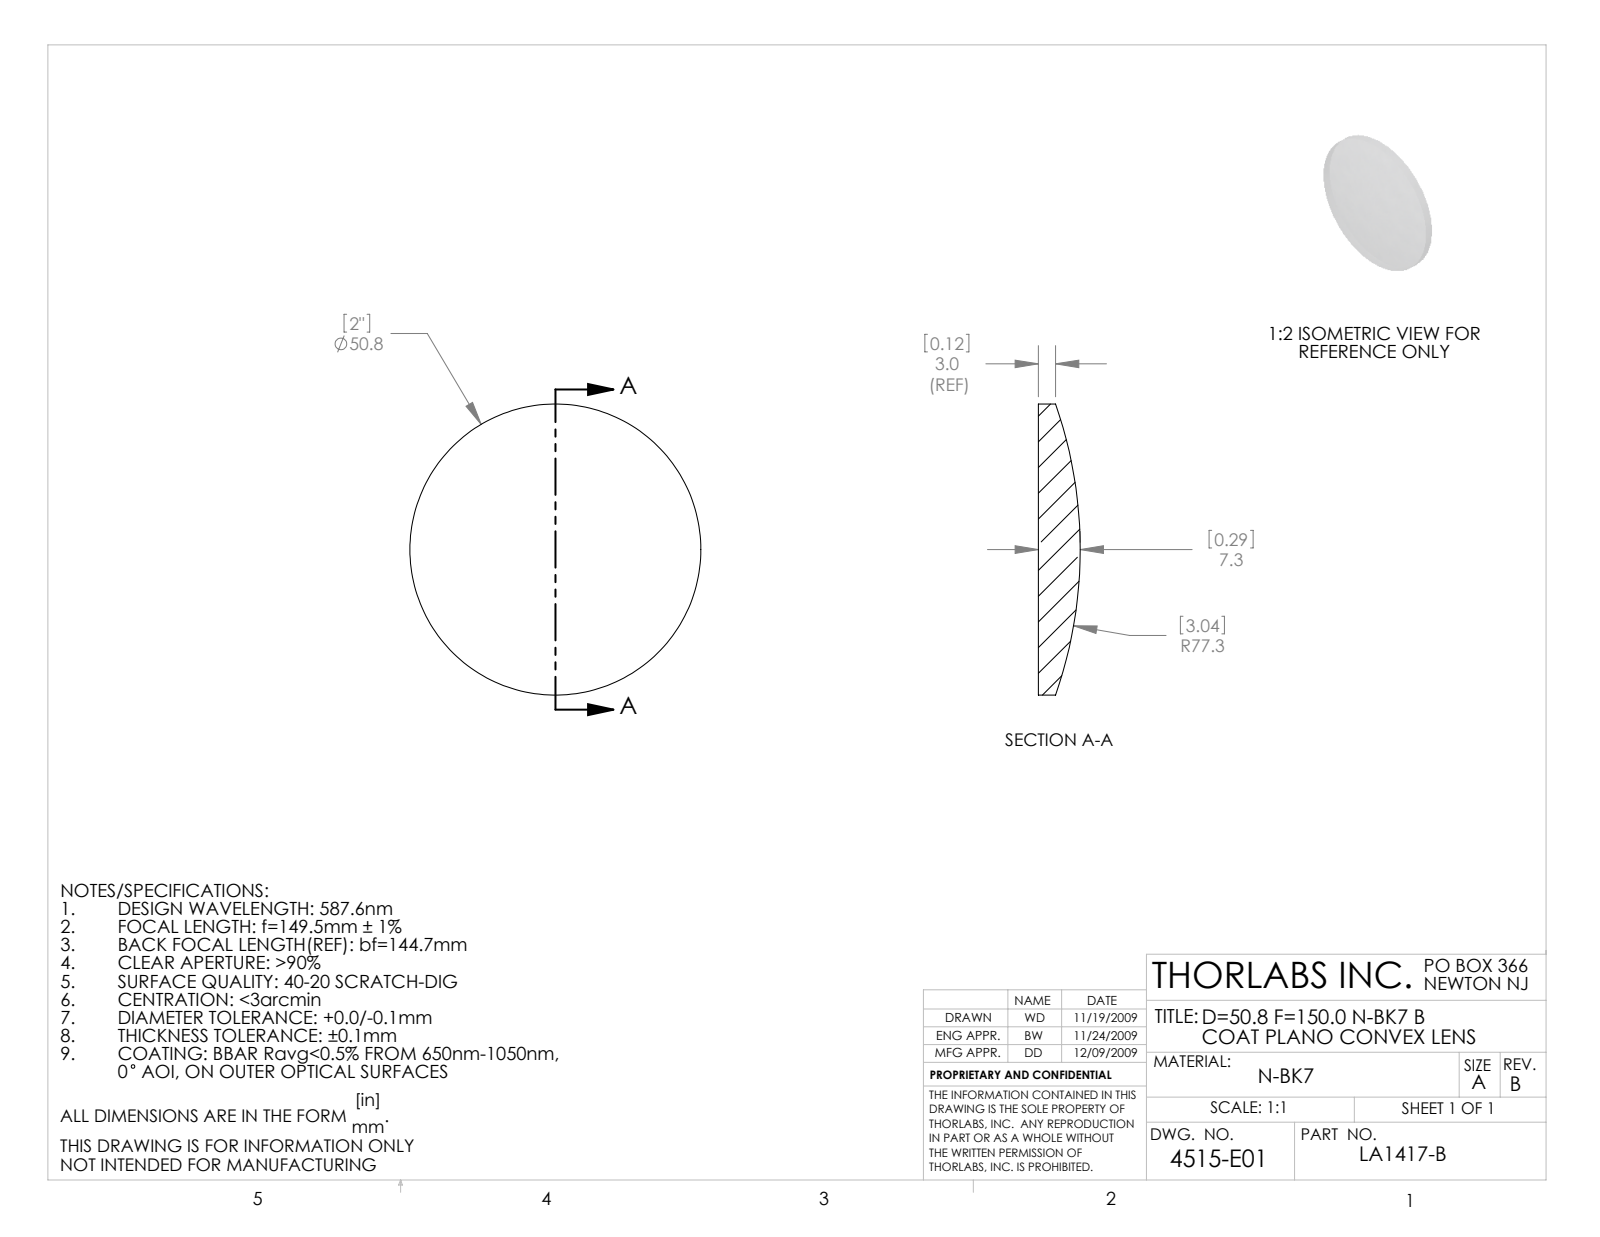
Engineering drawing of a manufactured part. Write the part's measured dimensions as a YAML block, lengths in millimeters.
part_name: "4515-E0W"
step_written_by: "SolidWorks 2009 (AUTOMOTIVE_DESIGN)"
units: millimeters
bodies: {solids: 1, faces: 5, planar: 1, cylindrical: 2, other: 2}
overall_size: [50.8, 50.8, 7.29]
volume: 10465
surface_area: 4590
round_bosses_or_shafts:
  - {diameter: 50.8, count: 1}
